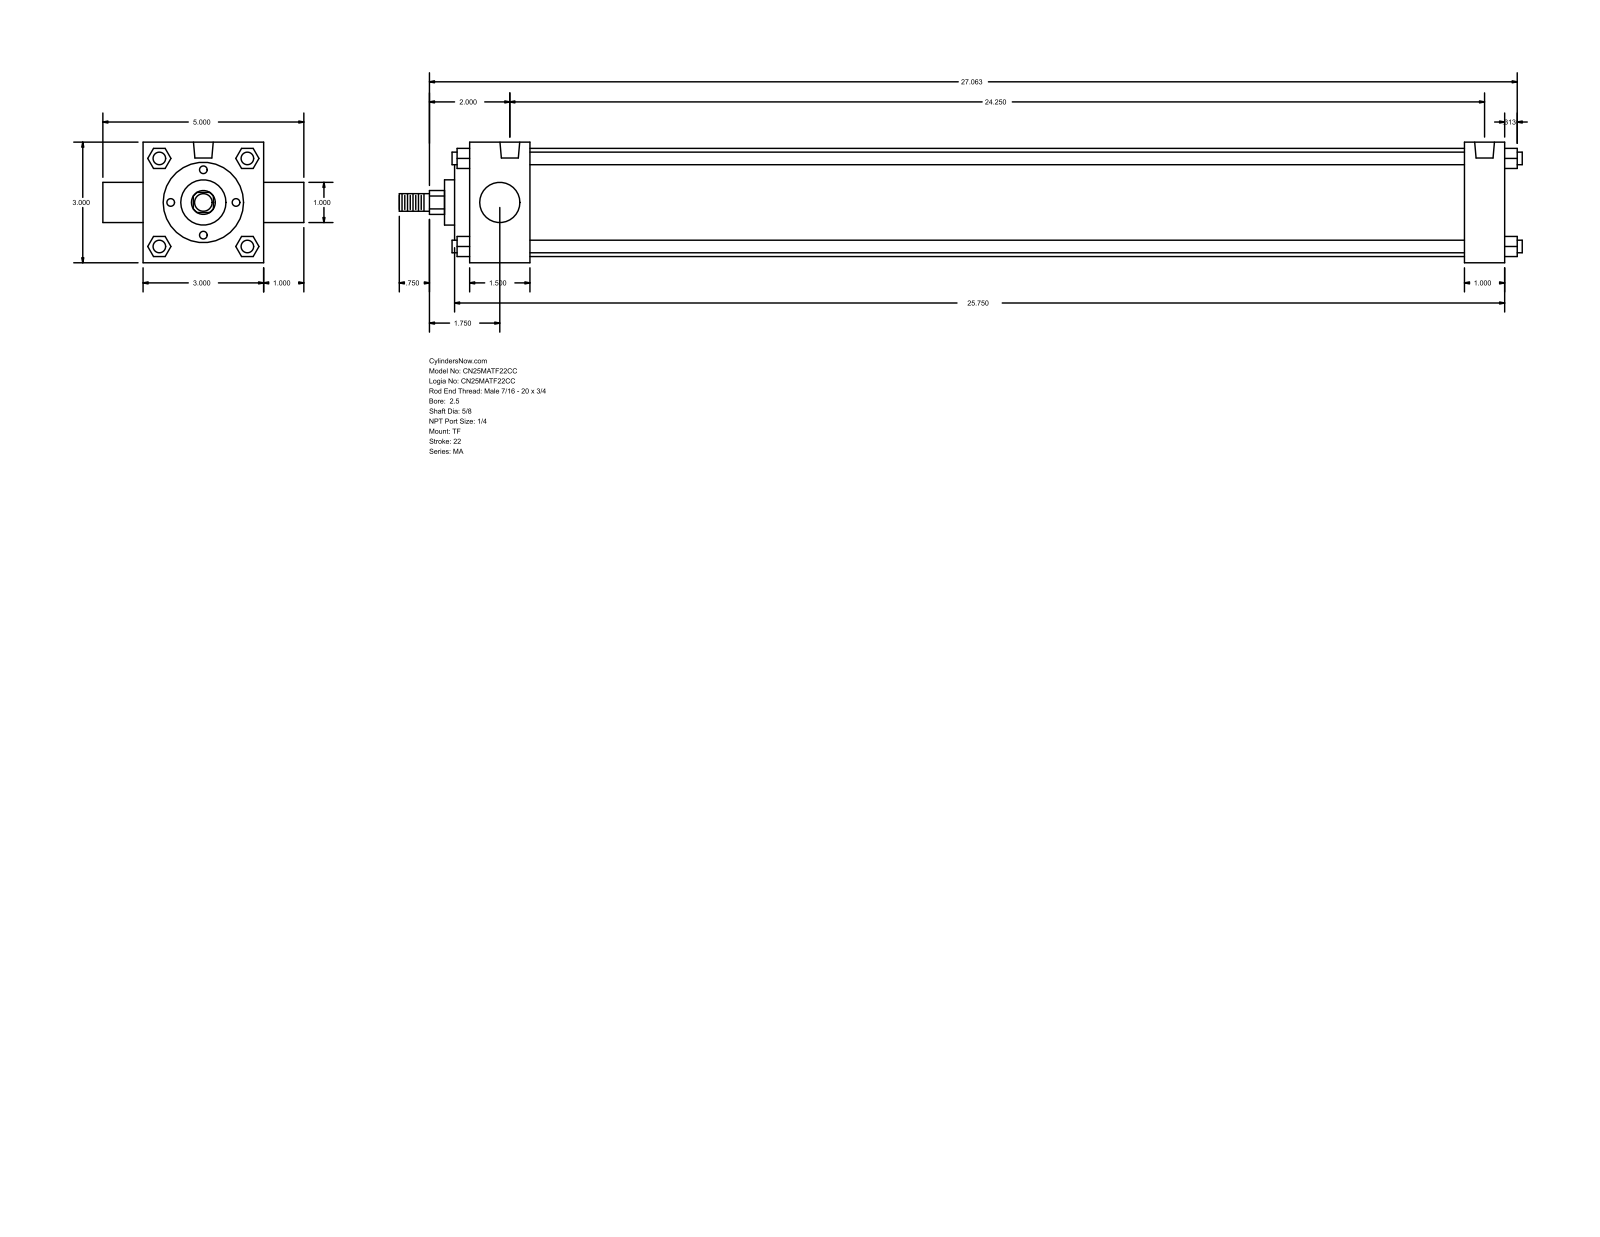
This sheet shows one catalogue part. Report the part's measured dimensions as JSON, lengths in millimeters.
{"part_name": "MA_TF__0250_0.625", "step_written_by": "GSSL Pune (CONFIG_CONTROL_DESIGN)", "units": "millimeters", "bodies": {"solids": 0, "faces": 122, "planar": 93, "cylindrical": 29, "other": 0}, "overall_size": [709.61, 127, 76.2], "round_holes": [[7.94, 3], [12.49, 2]], "round_bosses_or_shafts": [[7.94, 4], [68.33, 1], [50.8, 1], [28.57, 1], [25.4, 1], [15.88, 1], [11.11, 1]], "partial_cylinders_radius": [[7.54, 1]], "face_to_face_distances": [76.2, 654.05, 25.4, 38.1, 628.65, 590.55, 615.95, 12.7, 9.52, 47.62], "hole_center_spacings": [615.95]}
